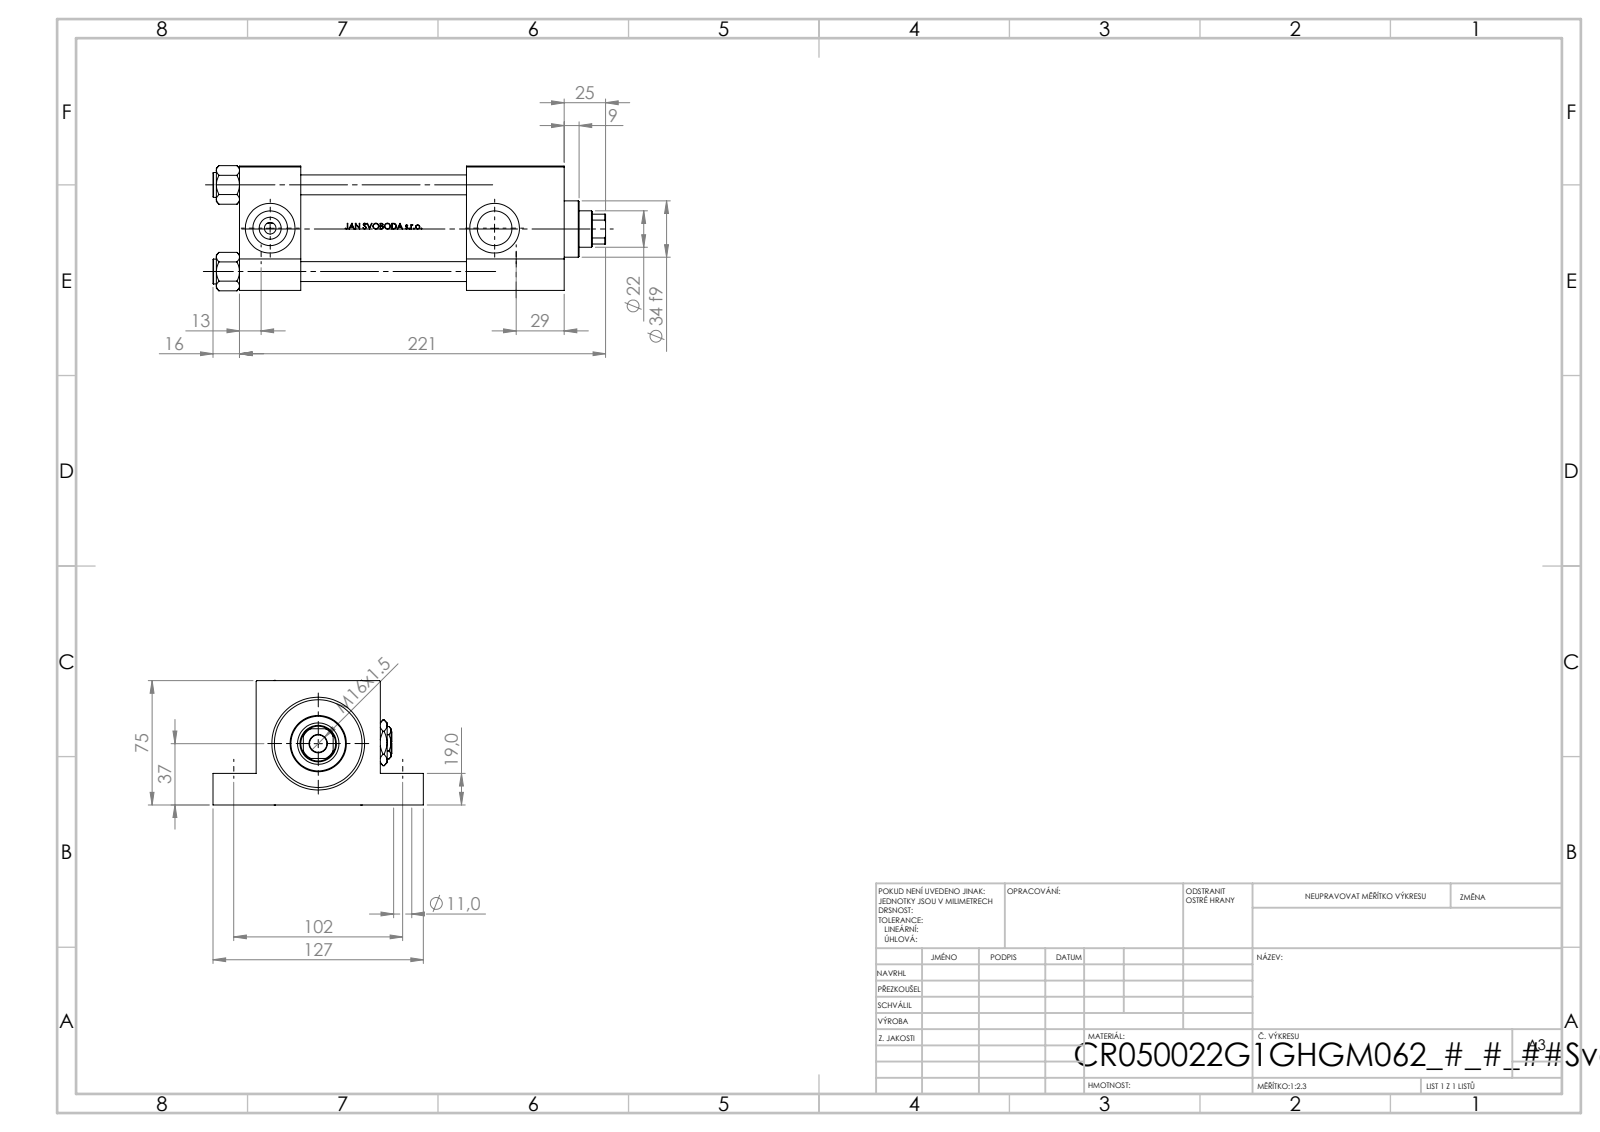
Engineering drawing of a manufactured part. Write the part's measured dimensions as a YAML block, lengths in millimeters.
part_name: "V215CR_VCP_G; Zatka_pro_OIL_PORT; NUT_M5_G; V215_VC_A (+2 more)"
step_written_by: "SolidWorks 2019 (CONFIG_CONTROL_DESIGN)"
units: millimeters
bodies: {solids: 12, faces: 1134, planar: 454, cylindrical: 128, other: 552}
overall_size: [237, 127, 75.54]
volume: 808349
surface_area: 184526
round_holes:
  - {diameter: 11, count: 4}
  - {diameter: 12, count: 4}
  - {diameter: 7, count: 2}
  - {diameter: 20.96, count: 2}
  - {diameter: 30, count: 2}
  - {diameter: 10.5, count: 1}
  - {diameter: 22, count: 1}
  - {diameter: 25, count: 1}
  - {diameter: 41, count: 1}
  - {diameter: 50, count: 1}
  - {diameter: 53, count: 1}
round_bosses_or_shafts:
  - {diameter: 15, count: 4}
  - {diameter: 56, count: 1}
  - {diameter: 34, count: 1}
partial_cylinders:
  - {radius: 10.5, count: 1}
face_to_face_distances: [75, 37, 196, 159, 19, 56, 137, 100, 59, 26]
hole_center_spacings: [52.3, 36.63, 37.34, 73.96, 102, 154, 184.72, 135.5]
